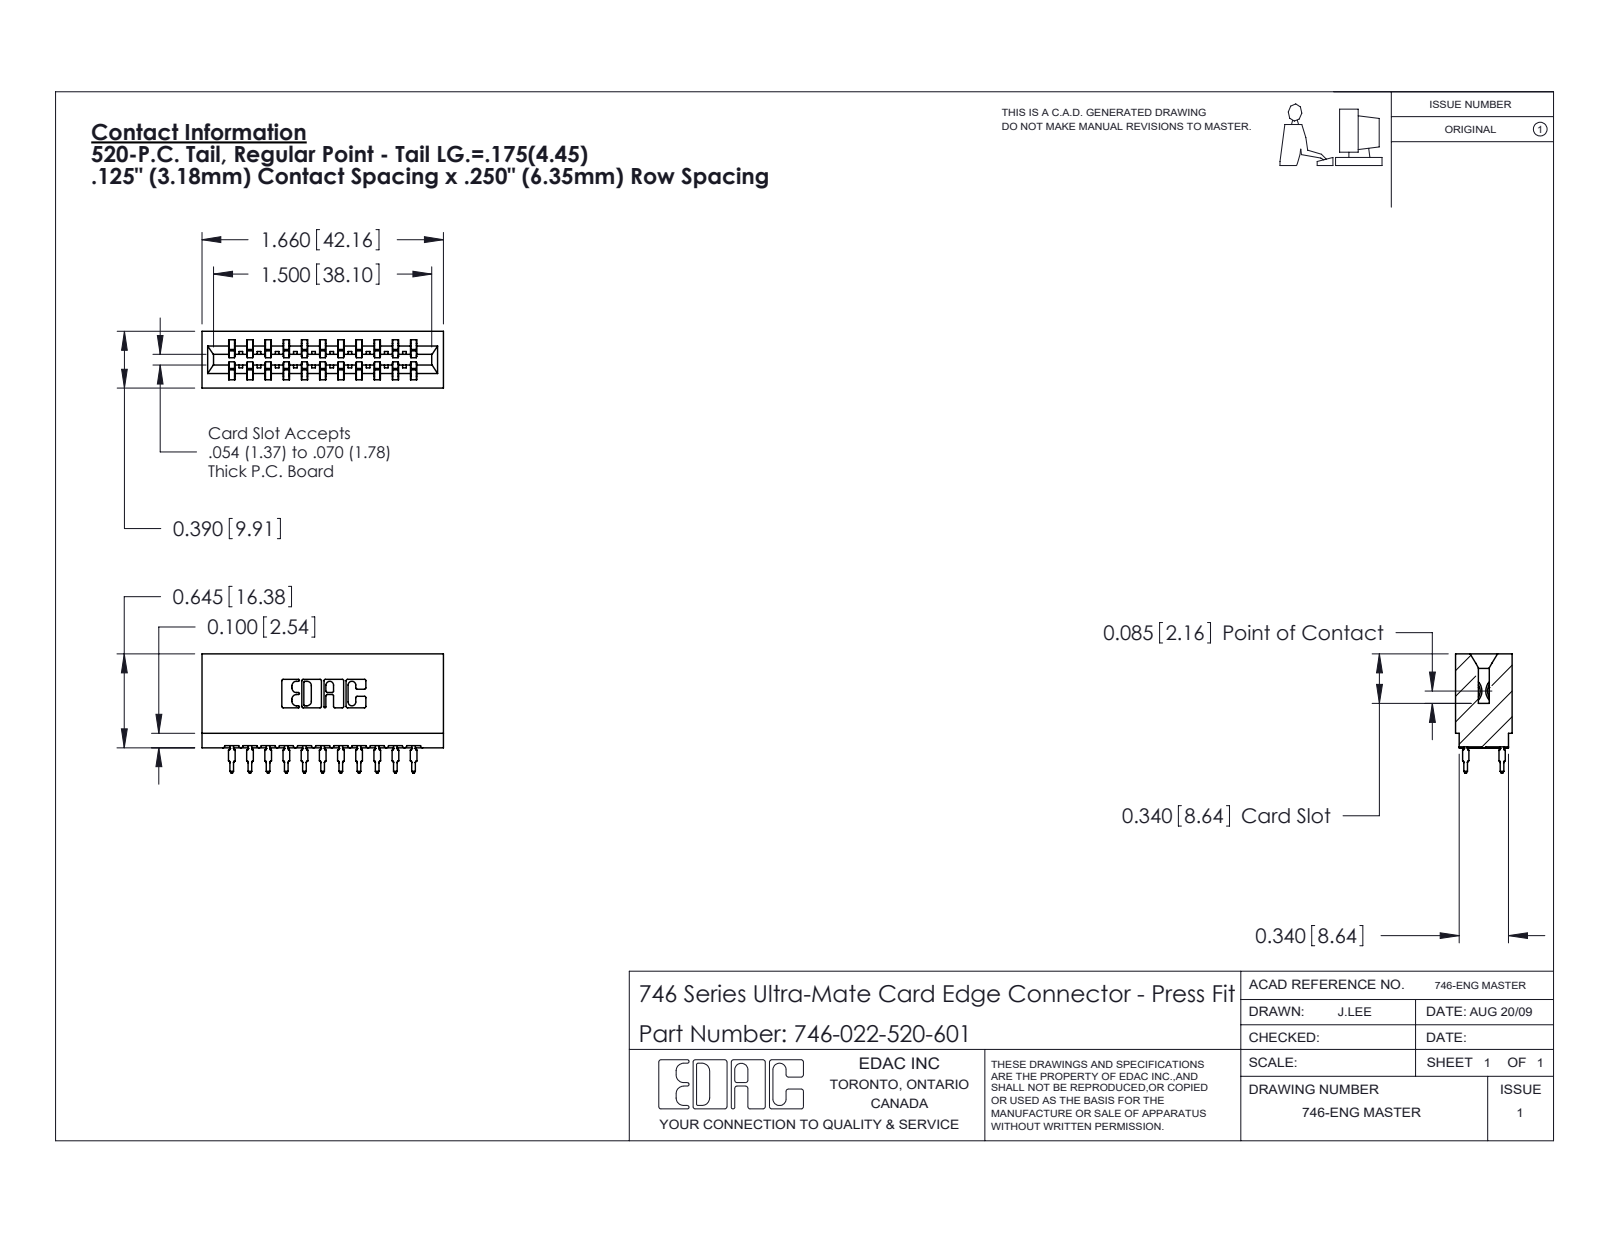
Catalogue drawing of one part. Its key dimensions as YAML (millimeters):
part_name: "746 Part_.340 Slot Depth - 01; 746-022-520-601; 746-292-001_520"
step_written_by: "SolidWorks 2020 (CONFIG_CONTROL_DESIGN)"
units: millimeters
bodies: {solids: 23, faces: 2066, planar: 1067, cylindrical: 427, other: 572}
overall_size: [42.2, 20.8, 9.9]
volume: 5000
surface_area: 6665
partial_cylinders:
  - {radius: 0.5, count: 44}
  - {radius: 0.3, count: 22}
  - {radius: 0.4, count: 12}
  - {radius: 0.1, count: 8}
  - {radius: 0.3, count: 8}
  - {radius: 0.2, count: 6}
  - {radius: 0.8, count: 6}
  - {radius: 0.7, count: 3}
face_to_face_distances: [6.4, 12.7, 1.4, 8.5, 3.2, 7.4, 3.2, 1.1, 13.8, 9.9]
